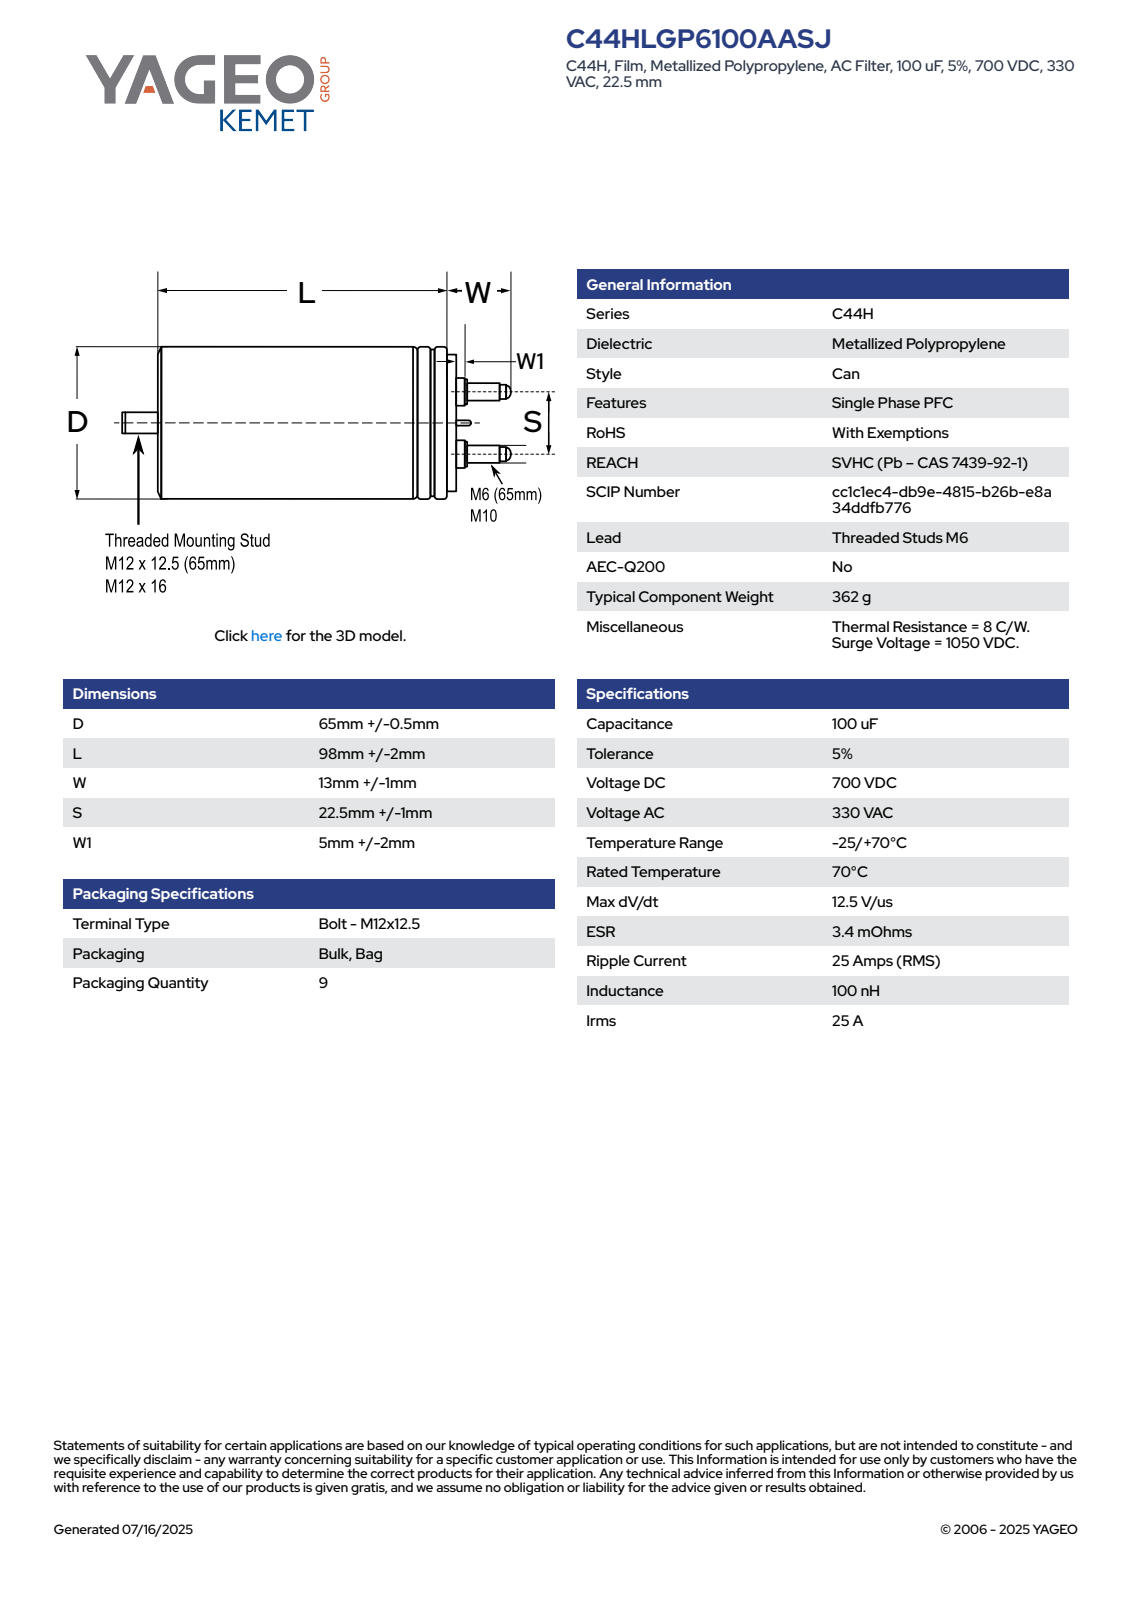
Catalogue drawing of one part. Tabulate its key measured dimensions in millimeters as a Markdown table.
| quantity | value |
| --- | --- |
| part name | CFP_C44H_65X98D65.5L100S22.5 |
| STEP written by | SolidWorks 2014 (AUTOMOTIVE_DESIGN) |
| units | millimeters |
| bodies | 1 solid, 104 faces (36 planar, 29 cylindrical, 39 other) |
| overall size | 132.5 × 65.51 × 65.5 |
| volume | 341 277 mm³ |
| surface area | 29 796 mm² |
| round holes (diameter × count) | 56.26 × 1 |
| round bosses / shafts (diameter × count) | 12 × 3, 6 × 2, 5.38 × 2, 65.5 × 1, 59.62 × 1 |
| partial cylindrical surfaces (radius × count) | 32.76 × 1 |
| main face-to-face distances | 100, 3, 103, 106, 6, 1.84, 12.5, 112.5, 115.5, 118.5 |
